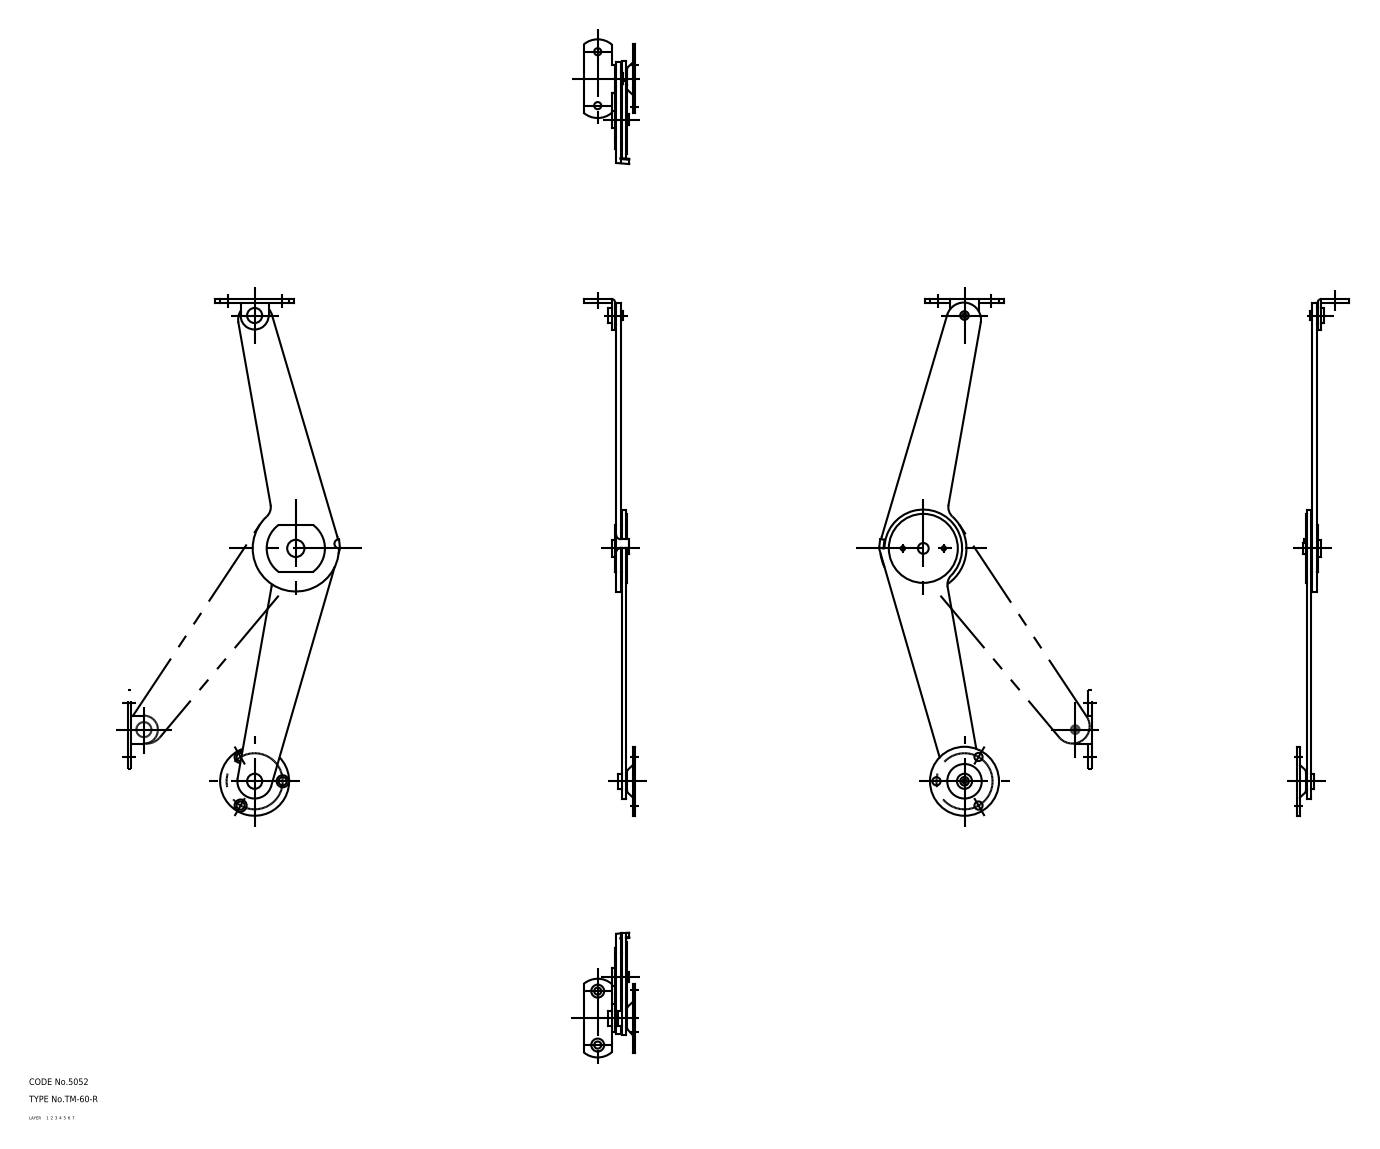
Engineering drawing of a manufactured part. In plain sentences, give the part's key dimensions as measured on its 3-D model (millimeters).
The part is named "ball_mr-1; washer_A_mr-1; washer_B_mr; washer_A_mr (+8 more)". Its 3-D file was written by "CADfix (AUTOMOTIVE_DESIGN)". It is 13 solids with 156 faces: 0 planar, 0 cylindrical and 156 other. Overall it measures 239.6 by 57.85 by 24 millimeters. Its volume is 16 003 cubic millimeters and its surface area 20 598 square millimeters.
